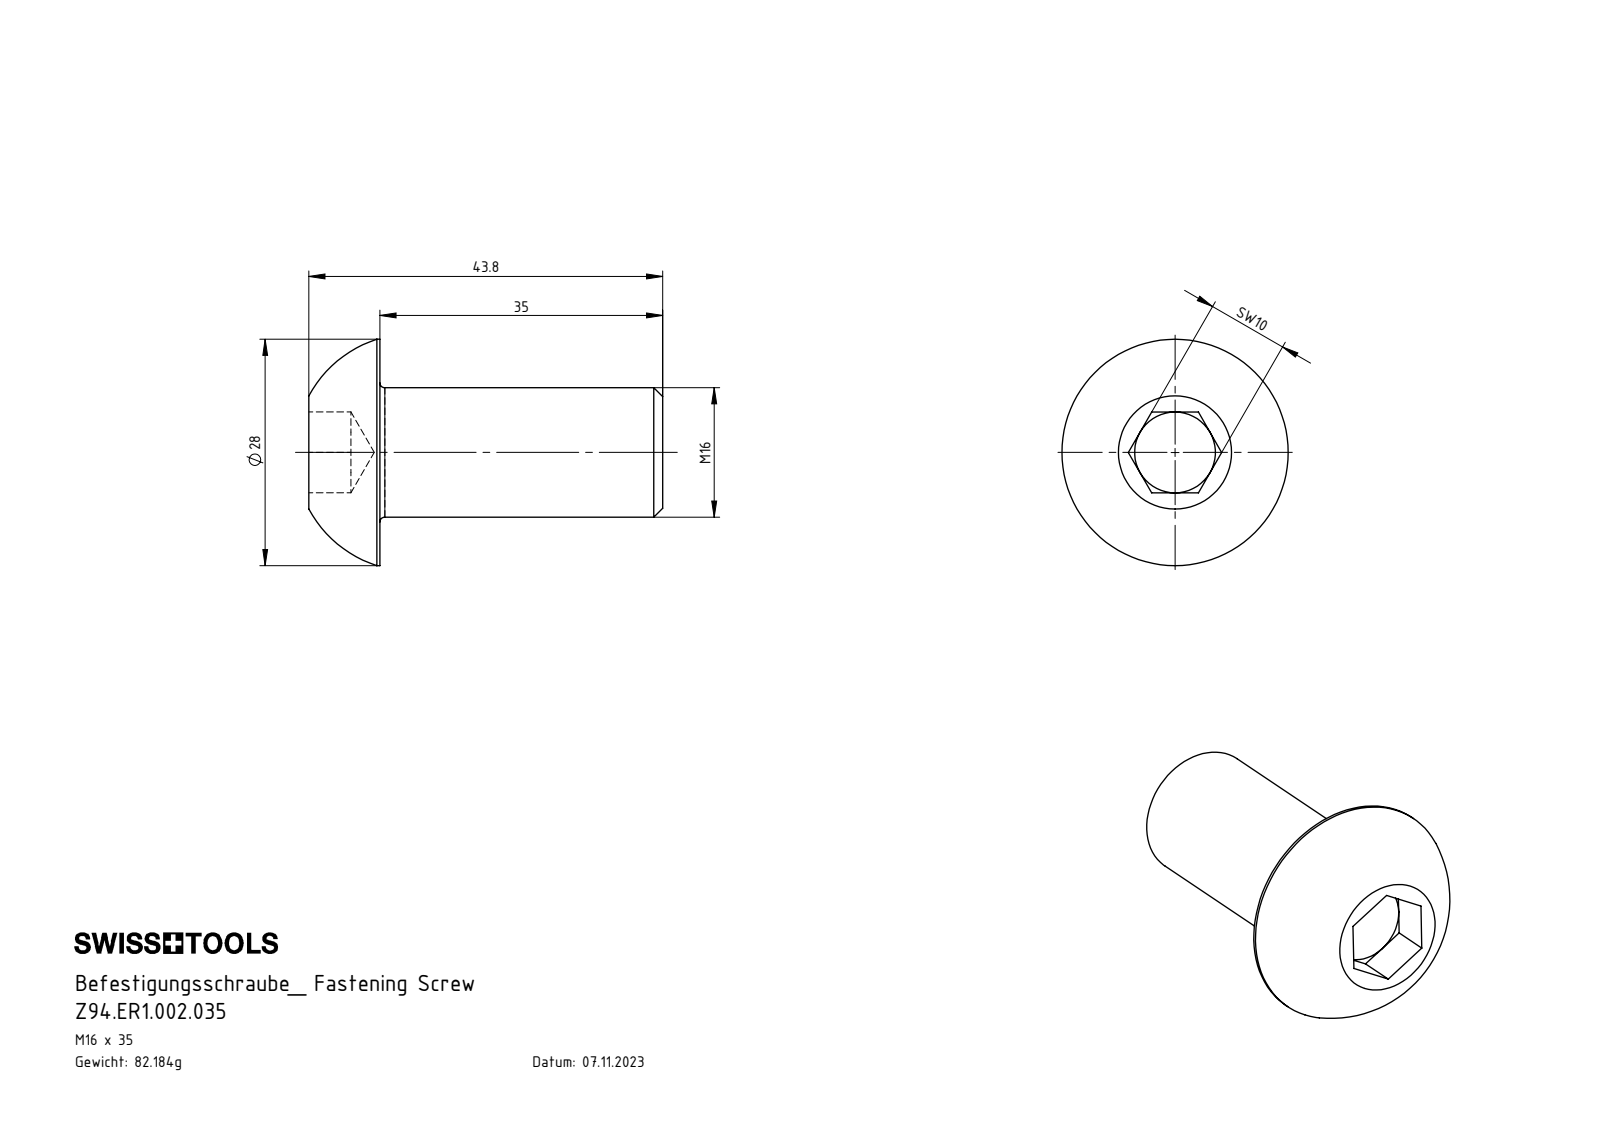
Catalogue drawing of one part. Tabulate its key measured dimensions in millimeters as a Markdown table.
| quantity | value |
| --- | --- |
| part name | Z94.ER1.002.035 |
| STEP written by | SolidWorks 2017 (AUTOMOTIVE_DESIGN) |
| units | millimeters |
| bodies | 0 solids, 2 faces (0 planar, 2 cylindrical, 0 other) |
| overall size | 33.3 × 16 × 16 |
| round bosses / shafts (diameter × count) | 16 × 1 |
